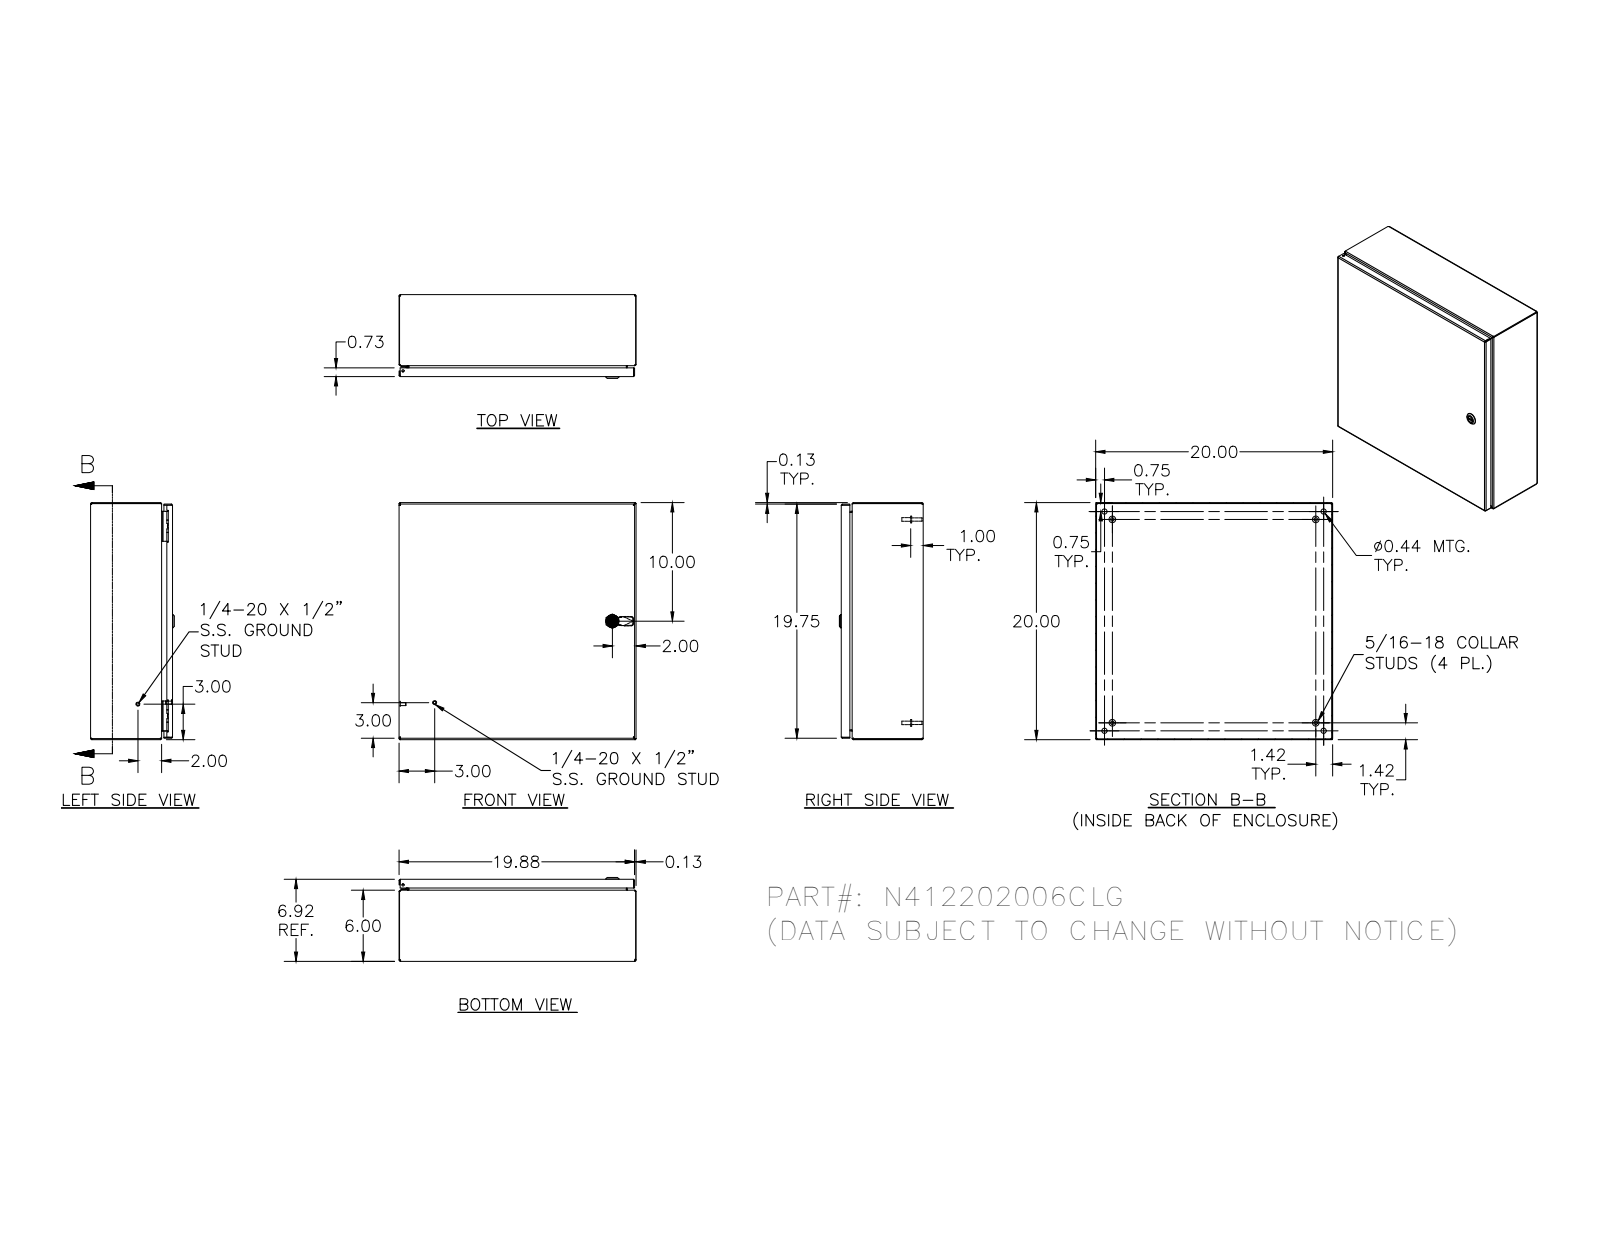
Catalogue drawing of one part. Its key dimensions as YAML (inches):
part_name: "N412202006CLG"
step_written_by: "SolidWorks 2018 (AUTOMOTIVE_DESIGN)"
units: inches
bodies: {solids: 33, faces: 1449, planar: 530, cylindrical: 547, other: 372}
overall_size: [20, 20, 7.075]
volume: 106.8
surface_area: 2906
round_holes:
  - {diameter: 0.188, count: 5}
  - {diameter: 0.093, count: 4}
  - {diameter: 0.152, count: 4}
  - {diameter: 0.167, count: 4}
  - {diameter: 0.172, count: 4}
  - {diameter: 0.437, count: 4}
  - {diameter: 0.156, count: 2}
  - {diameter: 0.187, count: 1}
  - {diameter: 0.197, count: 1}
  - {diameter: 0.315, count: 1}
  - {diameter: 0.394, count: 1}
  - {diameter: 0.402, count: 1}
round_bosses_or_shafts:
  - {diameter: 0.25, count: 10}
  - {diameter: 0.563, count: 4}
  - {diameter: 0.36, count: 4}
  - {diameter: 0.32, count: 4}
  - {diameter: 0.3, count: 4}
  - {diameter: 0.275, count: 4}
  - {diameter: 0.256, count: 4}
  - {diameter: 0.164, count: 4}
partial_cylinders:
  - {radius: 0.012, count: 30}
  - {radius: 0.031, count: 30}
  - {radius: 0.05, count: 26}
  - {radius: 0.105, count: 20}
  - {radius: 0.016, count: 18}
  - {radius: 0.125, count: 16}
  - {radius: 0.02, count: 13}
  - {radius: 0.032, count: 8}
face_to_face_distances: [0.074, 6.843, 6.769, 6.917, 19.926, 19.852, 0.074, 19.926, 20, 0.917]
hole_center_spacings: [16, 0.66, 0.656, 1.307, 1.965, 15.34, 16.66, 18.5]
